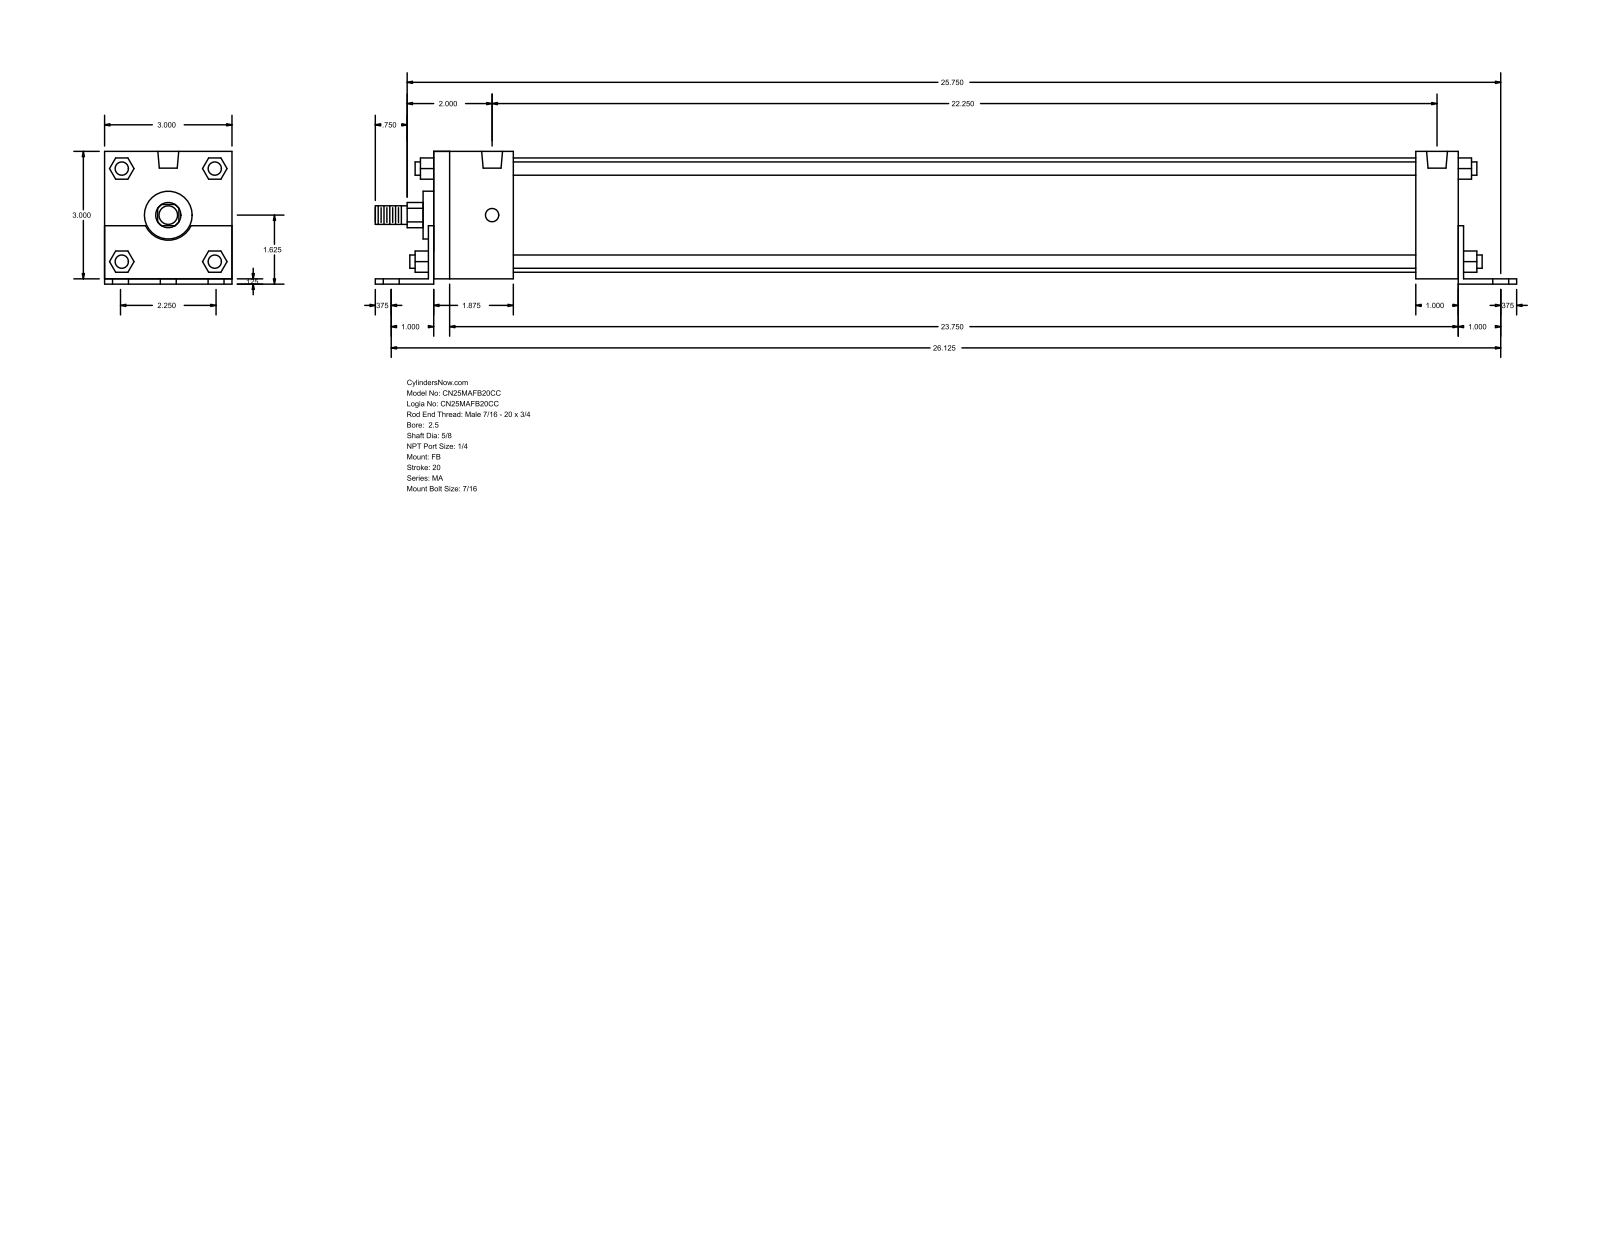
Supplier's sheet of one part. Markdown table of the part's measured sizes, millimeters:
| quantity | value |
| --- | --- |
| part name | MA_FB__0250_0.625 |
| STEP written by | GSSL Pune (CONFIG_CONTROL_DESIGN) |
| units | millimeters |
| bodies | 0 solids, 140 faces (105 planar, 35 cylindrical, 0 other) |
| overall size | 682.62 × 79.38 × 76.2 |
| round holes (diameter × count) | 11.11 × 6, 7.94 × 4, 12.49 × 2 |
| round bosses / shafts (diameter × count) | 7.94 × 4, 68.33 × 1, 28.57 × 1, 15.88 × 1, 11.11 × 1 |
| partial cylindrical surfaces (radius × count) | 7.54 × 1, 15.05 × 1 |
| main face-to-face distances | 76.2, 3.17, 79.37, 3.18, 615.95, 612.77, 28.58, 47.62, 25.4, 619.13 |
| hole center spacings | 28.57, 664.19, 663.58, 47.62, 57.14, 66.75, 565.15, 603.93 |
